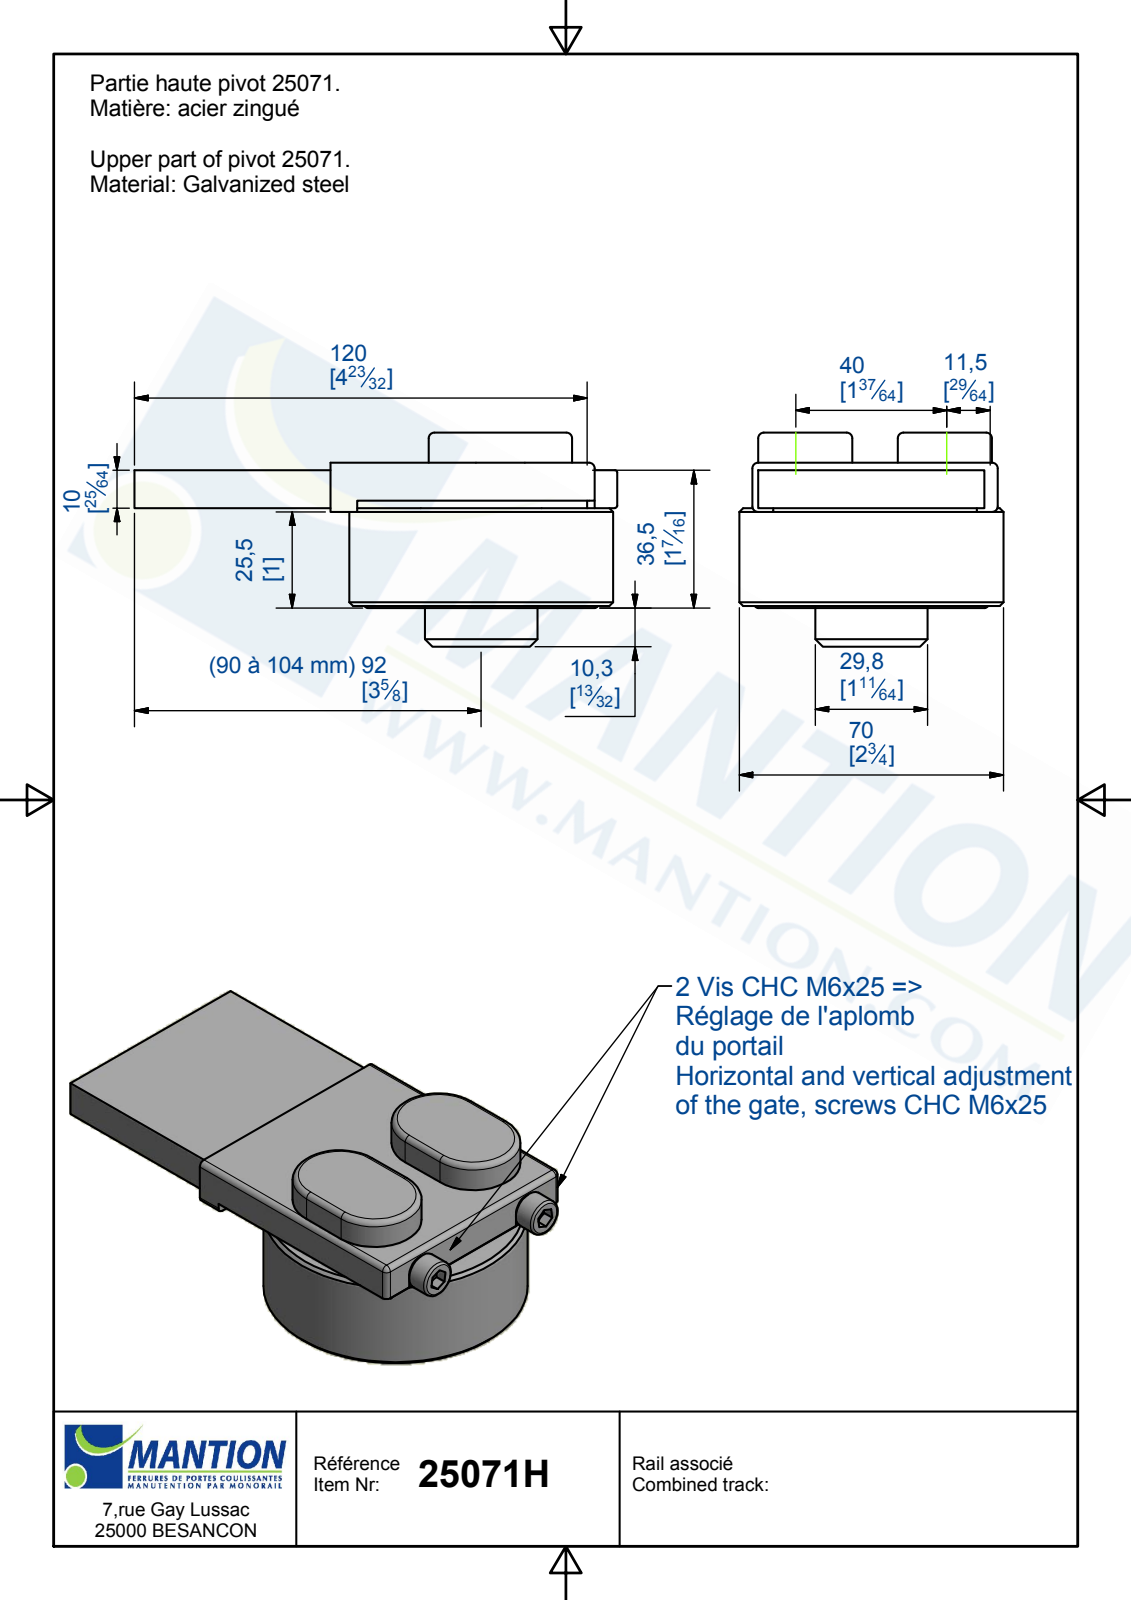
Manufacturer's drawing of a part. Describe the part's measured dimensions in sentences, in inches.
The part is named "Pièce235". Its 3-D file was written by "Autodesk Inventor 2019 (AUTOMOTIVE_DESIGN)". It is 13 solids with 376 faces: 228 planar, 69 cylindrical and 79 other. Overall it measures 5.118 by 3.024 by 2.756 inches. Its volume is 10.61 cubic inches and its surface area 128.9 square inches. Round holes: 2 of diameter 0.194, 2 of diameter 0.33, 2 of diameter 0.402, 1 of diameter 1.181, 1 of diameter 1.507, 1 of diameter 1.923, 1 of diameter 2.032, 1 of diameter 2.362, 1 of diameter 2.52. Round bosses or shafts: 4 of diameter 0.394, 2 of diameter 0.709, 2 of diameter 0.236, 1 of diameter 2.756, 1 of diameter 2.441, 1 of diameter 1.699, 1 of diameter 1.457, 1 of diameter 1.173. Partial cylindrical surfaces (rounded edges, fillets, slot ends): 14 of radius 0.008, 11 of radius 0.059, 4 of radius 0.236, 4 of radius 0.413, 4 of radius 0.492, 2 of radius 0.157. The main face-to-face distances are 0.394, 0.079, 1.181, 0.681, 0.287, 0.315, 0.866, 0.787, 1.469, 1.26. The hole center spacings are 1.575, 0.787, 0.071, 0.789.
